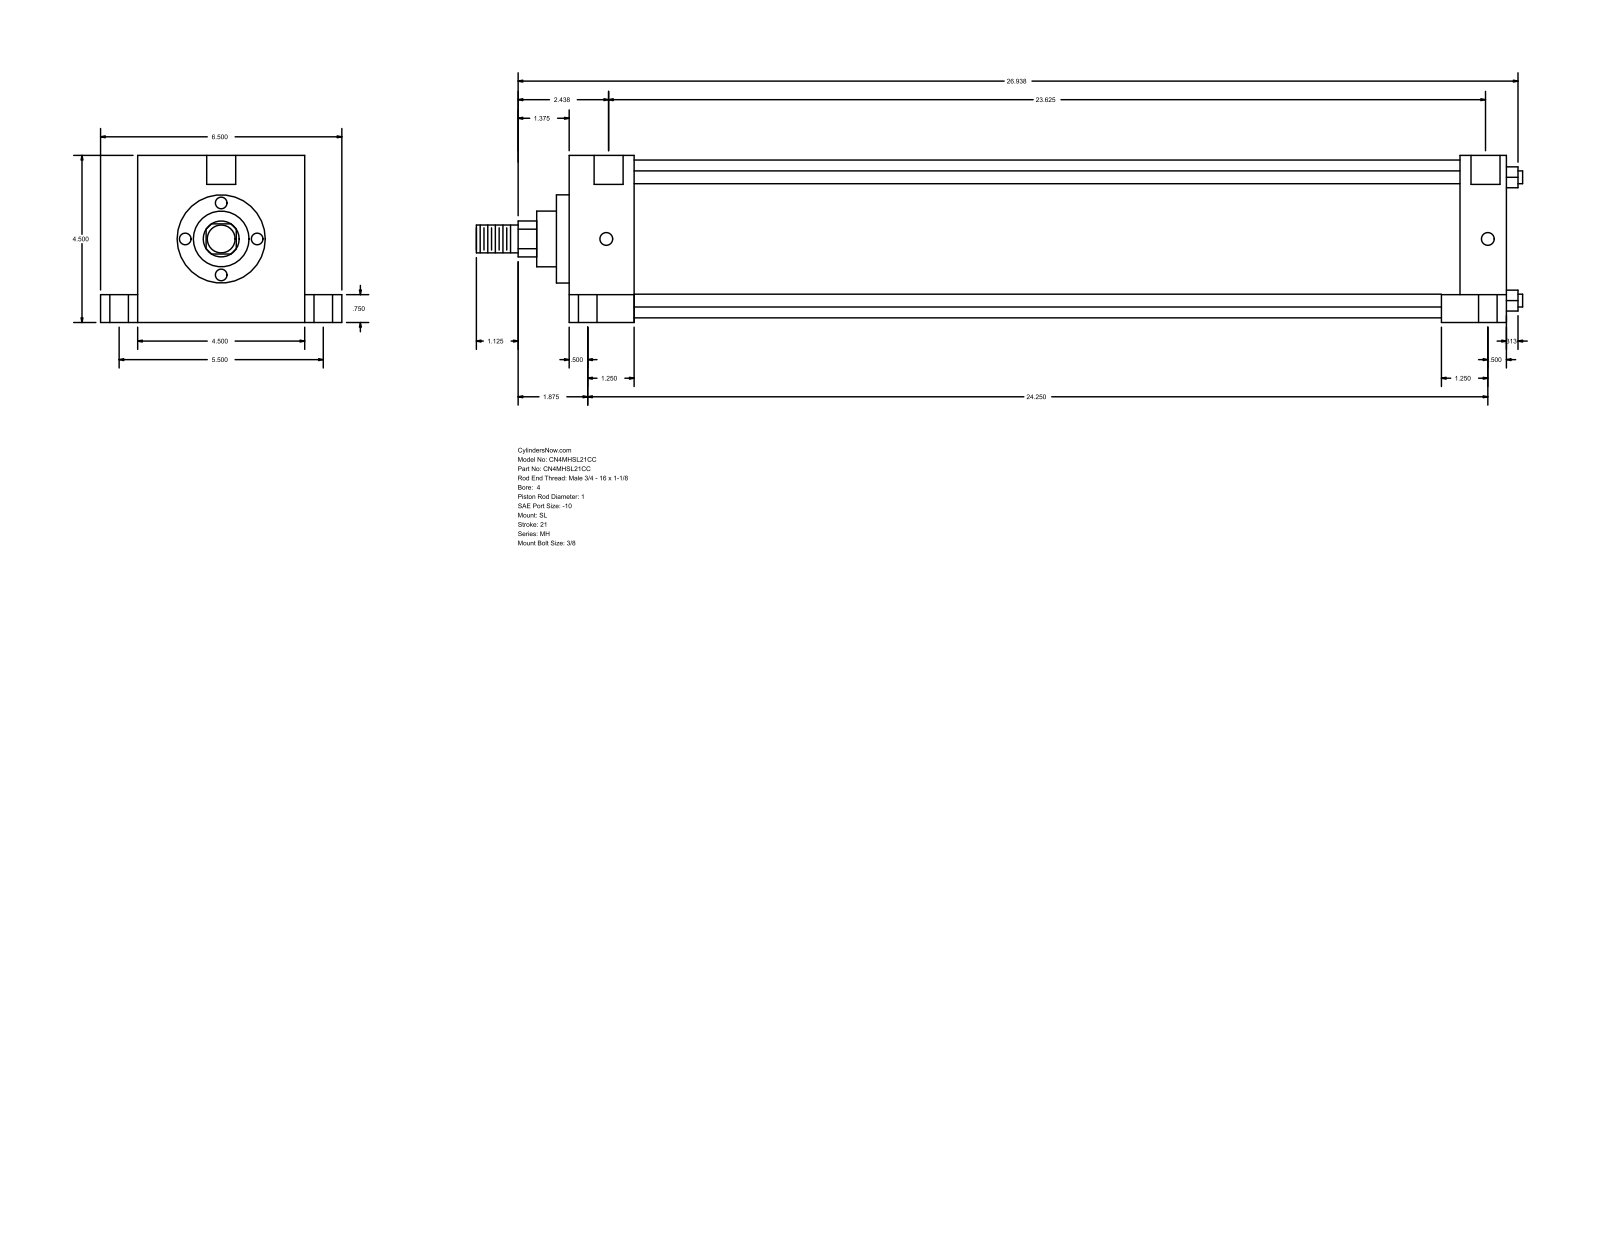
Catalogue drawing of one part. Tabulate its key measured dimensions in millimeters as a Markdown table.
| quantity | value |
| --- | --- |
| part name | MH_SL__0400_1 |
| STEP written by | GSSL Pune (CONFIG_CONTROL_DESIGN) |
| units | millimeters |
| bodies | 0 solids, 110 faces (77 planar, 33 cylindrical, 0 other) |
| overall size | 715.96 × 165.1 × 114.3 |
| round holes (diameter × count) | 8.73 × 4, 12.7 × 4, 19.05 × 4, 19.84 × 2 |
| round bosses / shafts (diameter × count) | 8.76 × 4, 107.95 × 1, 60.33 × 1, 38.1 × 1, 25.4 × 1, 19.05 × 1 |
| partial cylindrical surfaces (radius × count) | 12.29 × 1 |
| main face-to-face distances | 114.3, 641.35, 44.46, 596.89, 609.6, 565.14, 31.75, 25.4, 139.7, 19.05 |
| hole center spacings | 69.85, 69.87, 71, 71.3, 139.7, 603.25, 605.71, 607.28 |
